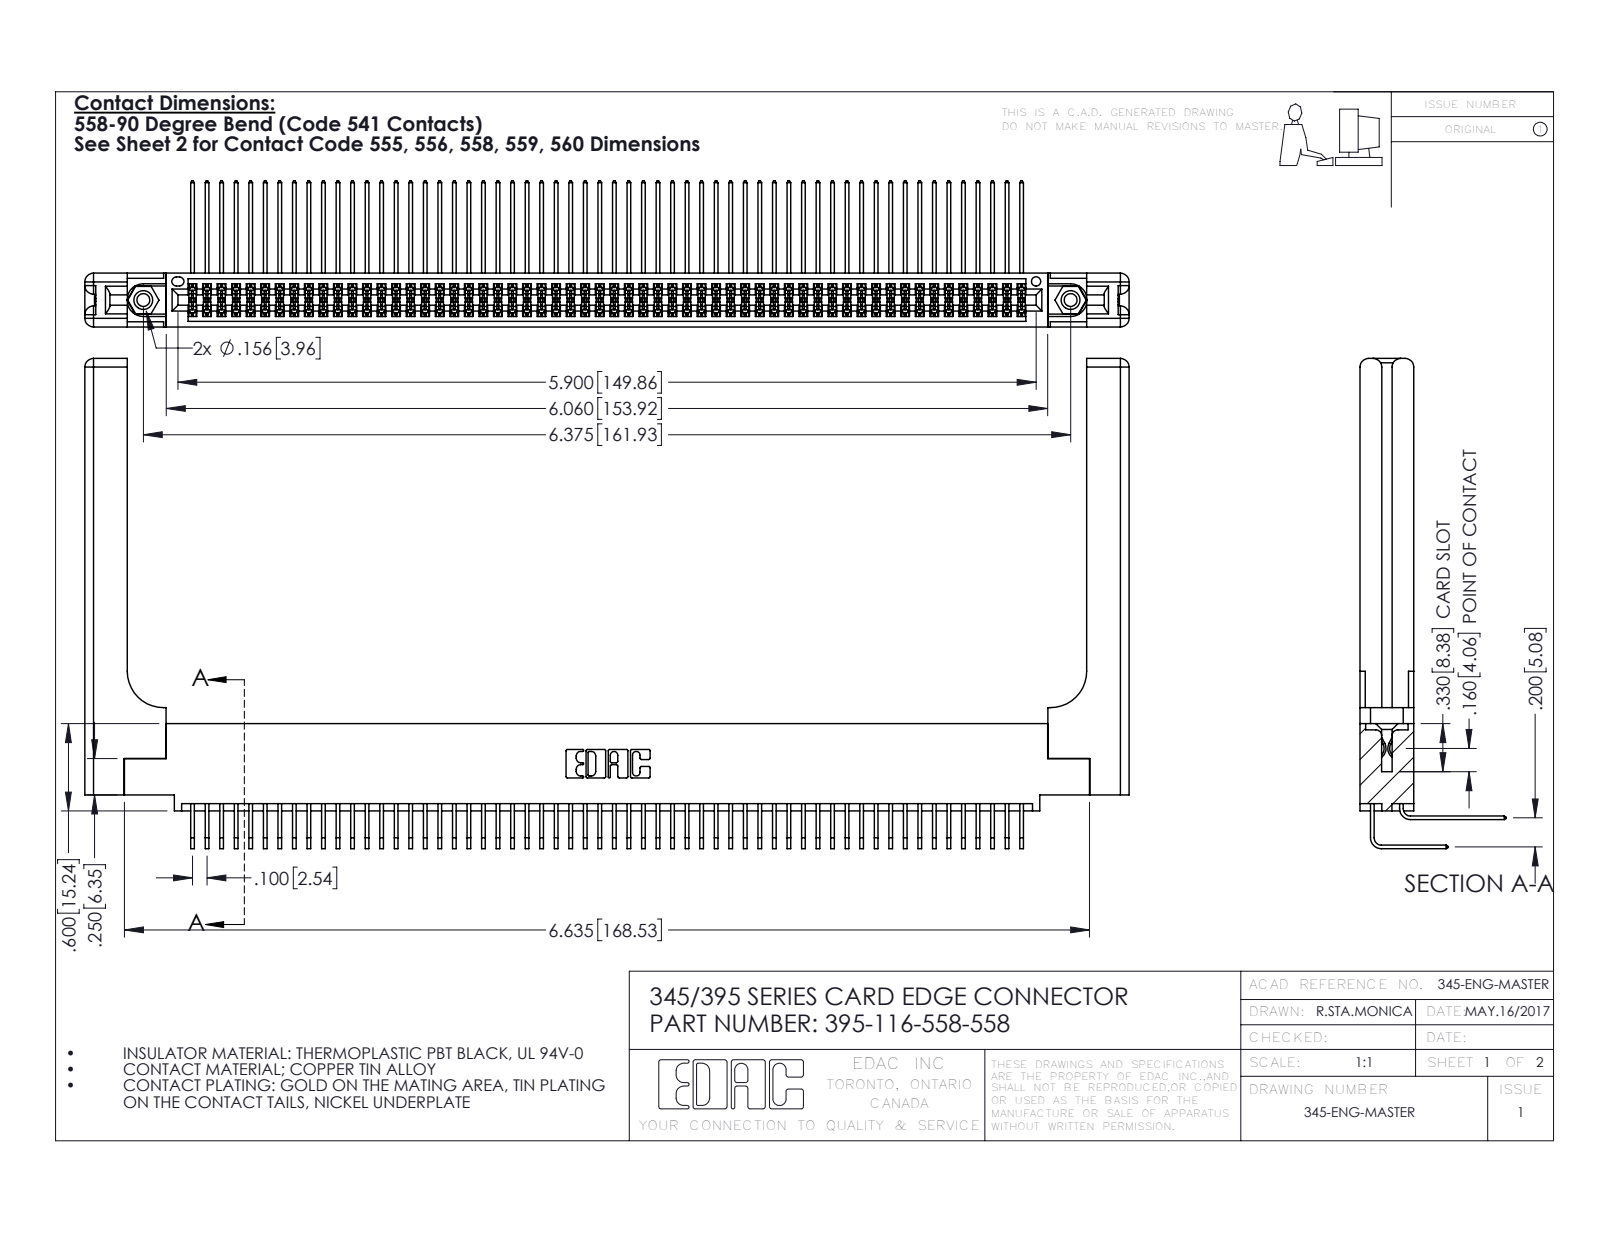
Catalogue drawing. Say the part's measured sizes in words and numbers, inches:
The part is named "345 Part_0.110 Offset - 0.156 Dia-TH; 345-292-001_558 559 Tail - 1; 345-220-058_345-220-058; 395-116-558-558 (+2 more)". Its 3-D file was written by "SolidWorks 2016 (CONFIG_CONTROL_DESIGN)". It is 121 solids with 6418 faces: 4292 planar, 2066 cylindrical and 60 other. Overall it measures 7.179 by 3.369 by 1.005 inches. Its volume is 1.644 cubic inches and its surface area 55.63 square inches. Round holes: 2 of diameter 0.089, 2 of diameter 0.125, 2 of diameter 0.156, 1 of diameter 0.064. Round bosses or shafts: 2 of diameter 0.155. Partial cylindrical surfaces (rounded edges, fillets, slot ends): 174 of radius 0.006, 22 of radius 0.01, 16 of radius 0.06, 6 of radius 0.007, 6 of radius 0.031, 3 of radius 0.026, 2 of radius 0.014, 2 of radius 0.019. The main face-to-face distances are 0.072, 0.298, 0.37, 0.2, 0.098, 0.272, 0.025, 0.225, 0.148, 0.15. The hole center spacings are 0.27, 6.139, 6.375.
